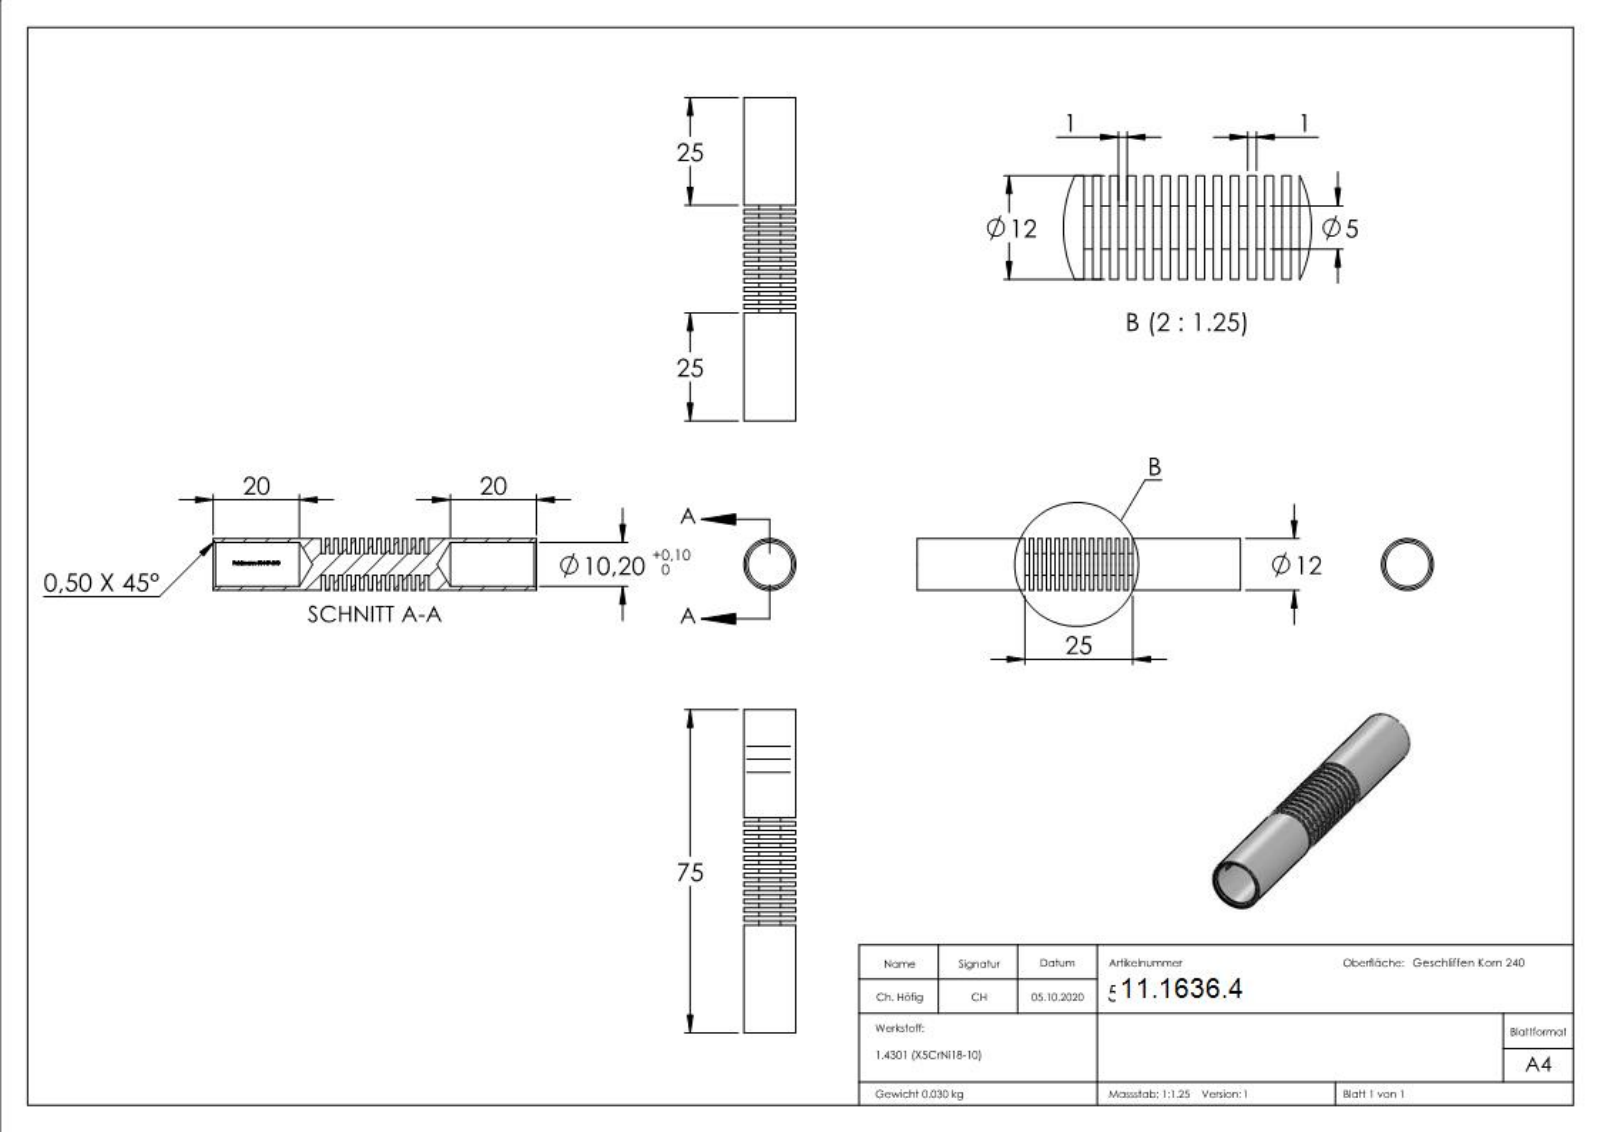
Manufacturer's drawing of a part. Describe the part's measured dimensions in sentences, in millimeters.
The part is named "50449-240". Its 3-D file was written by "SolidWorks 2018 (CONFIG_CONTROL_DESIGN)". It is 1 solid with 327 faces: 140 planar, 90 cylindrical and 97 other. Overall it measures 75 by 12 by 12 millimeters. Its volume is 3 823 cubic millimeters and its surface area 6 494 square millimeters. Round holes: 1 of diameter 10.2. Round bosses or shafts: 1 of diameter 12, 1 of diameter 5. Partial cylindrical surfaces (rounded edges, fillets, slot ends): 1 of radius 5.2. The main face-to-face distances are 1, 2, 3, 4, 5, 6, 7, 8, 9, 10.
